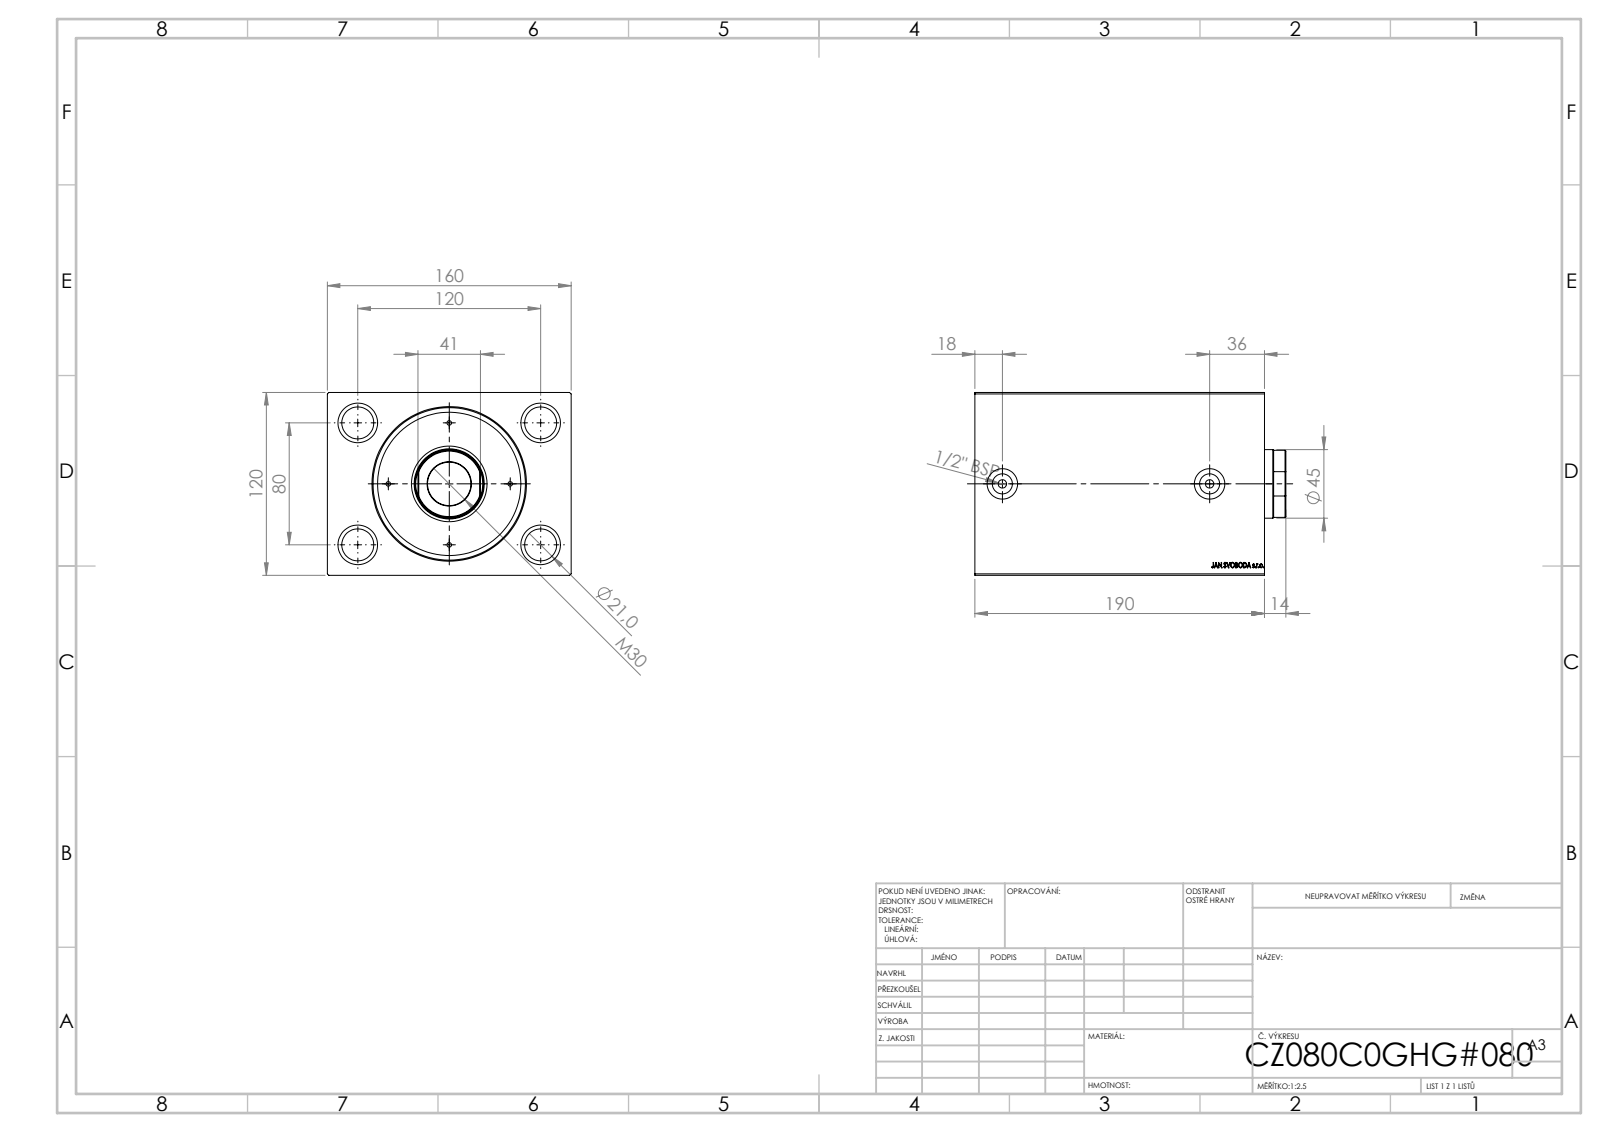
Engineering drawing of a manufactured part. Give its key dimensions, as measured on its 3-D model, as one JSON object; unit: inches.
{"step_written_by": "SolidWorks 2019 (CONFIG_CONTROL_DESIGN)", "units": "inches", "bodies": {"solids": 1, "faces": 825, "planar": 397, "cylindrical": 46, "other": 382}, "overall_size": [7.48, 6.299, 4.724], "volume_in3": 152.4, "surface_area_in2": 367, "round_holes": [[0.827, 4], [1.024, 4], [0.217, 2], [0.315, 2], [0.518, 2], [0.787, 2], [1.417, 1], [3.15, 1], [3.937, 1]], "face_to_face_distances": [4.724, 6.299, 7.48, 6.484, 0.996, 0.551, 5.933, 6.929, 0.407, 7.074], "hole_center_spacings": [2.839, 3.15, 4.724, 5.678, 4.567, 5.354]}
